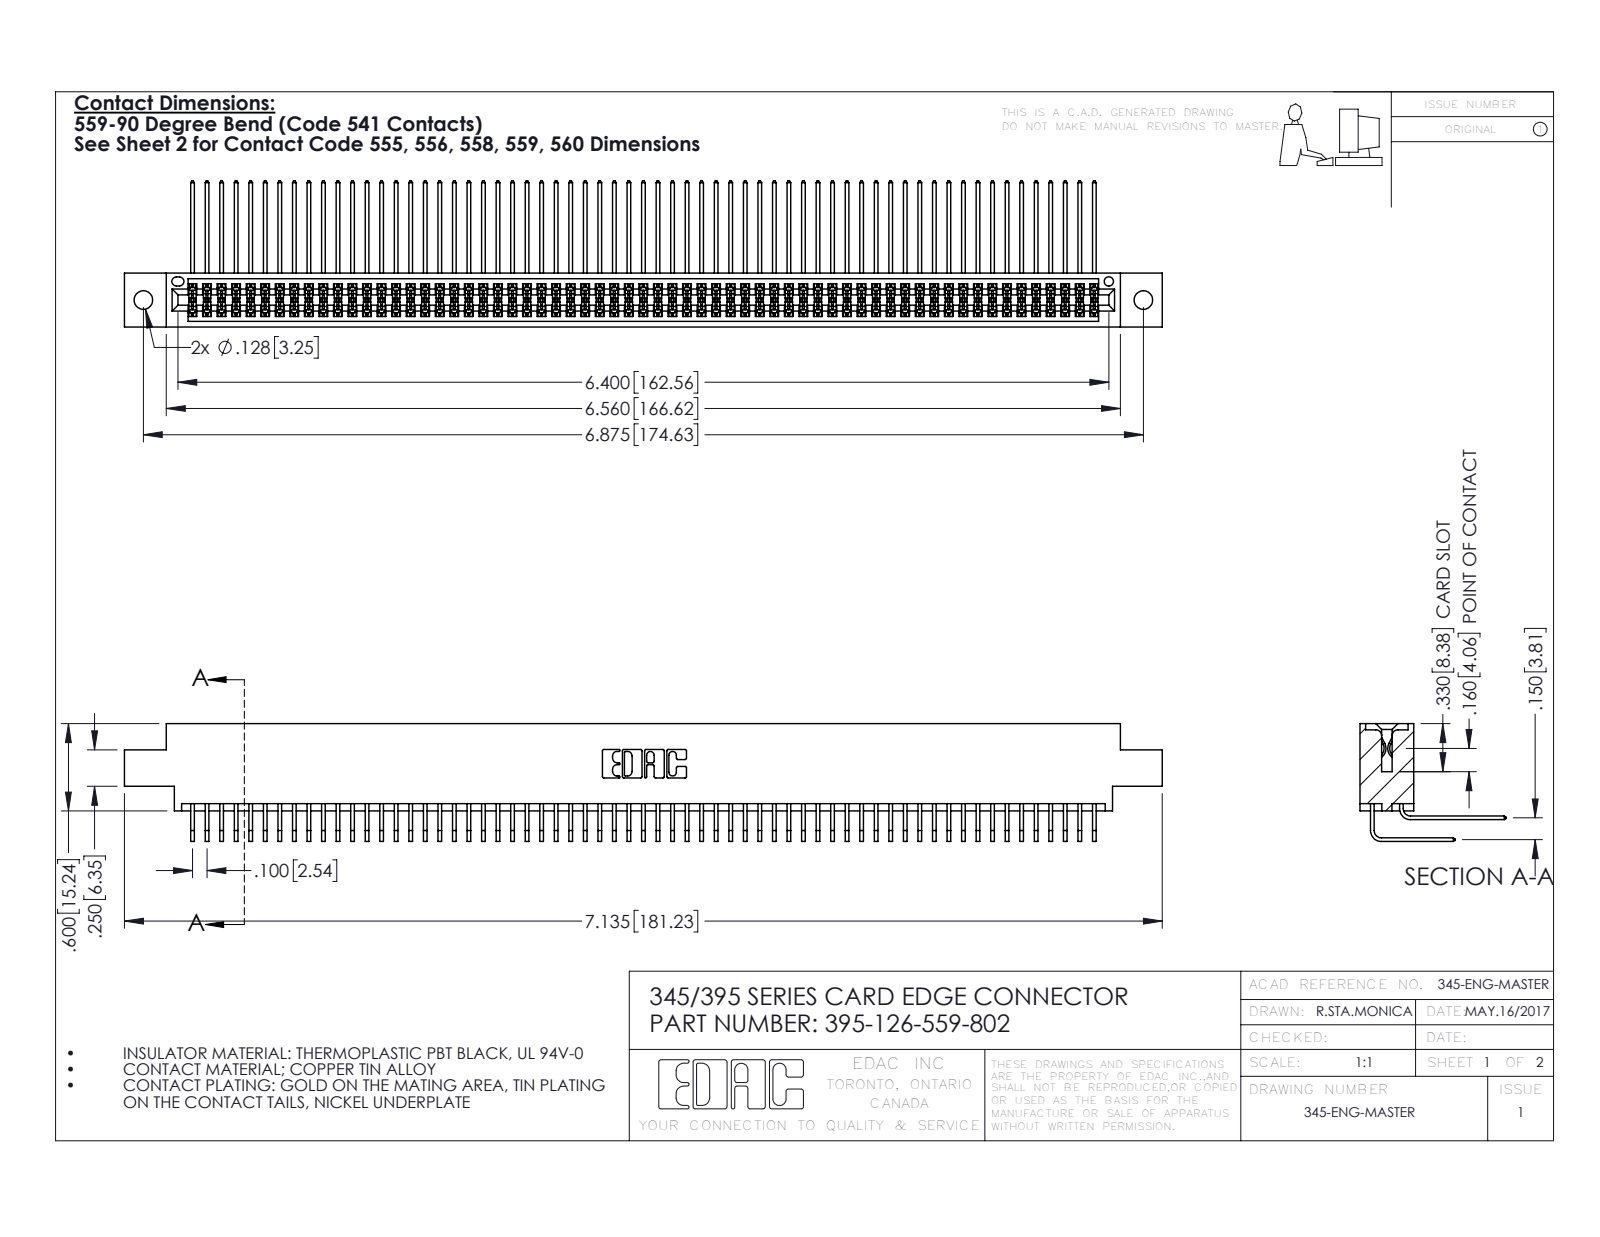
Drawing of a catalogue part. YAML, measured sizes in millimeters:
part_name: "395-126-559-802; 345-292-001_558 559 Tail - 1; 345-292-001_559 Tail - 2; 345 Part_0.170 Offset - 0.128 Dia"
step_written_by: "SolidWorks 2016 (CONFIG_CONTROL_DESIGN)"
units: millimeters
bodies: {solids: 127, faces: 6682, planar: 4494, cylindrical: 2188, other: 0}
overall_size: [181.2, 25.5, 20.5]
volume: 18370
surface_area: 30860
round_holes:
  - {diameter: 3.3, count: 2}
  - {diameter: 1.6, count: 1}
partial_cylinders:
  - {radius: 0.2, count: 189}
  - {radius: 0.3, count: 22}
  - {radius: 0.2, count: 6}
  - {radius: 0.8, count: 6}
  - {radius: 0.7, count: 3}
  - {radius: 0.4, count: 2}
  - {radius: 0.5, count: 2}
  - {radius: 0.6, count: 2}
face_to_face_distances: [1.8, 7.6, 9.4, 5.1, 2.5, 6.9, 0.6, 5.7, 4.4, 3.8]
hole_center_spacings: [6.9, 168.6, 174.6]
